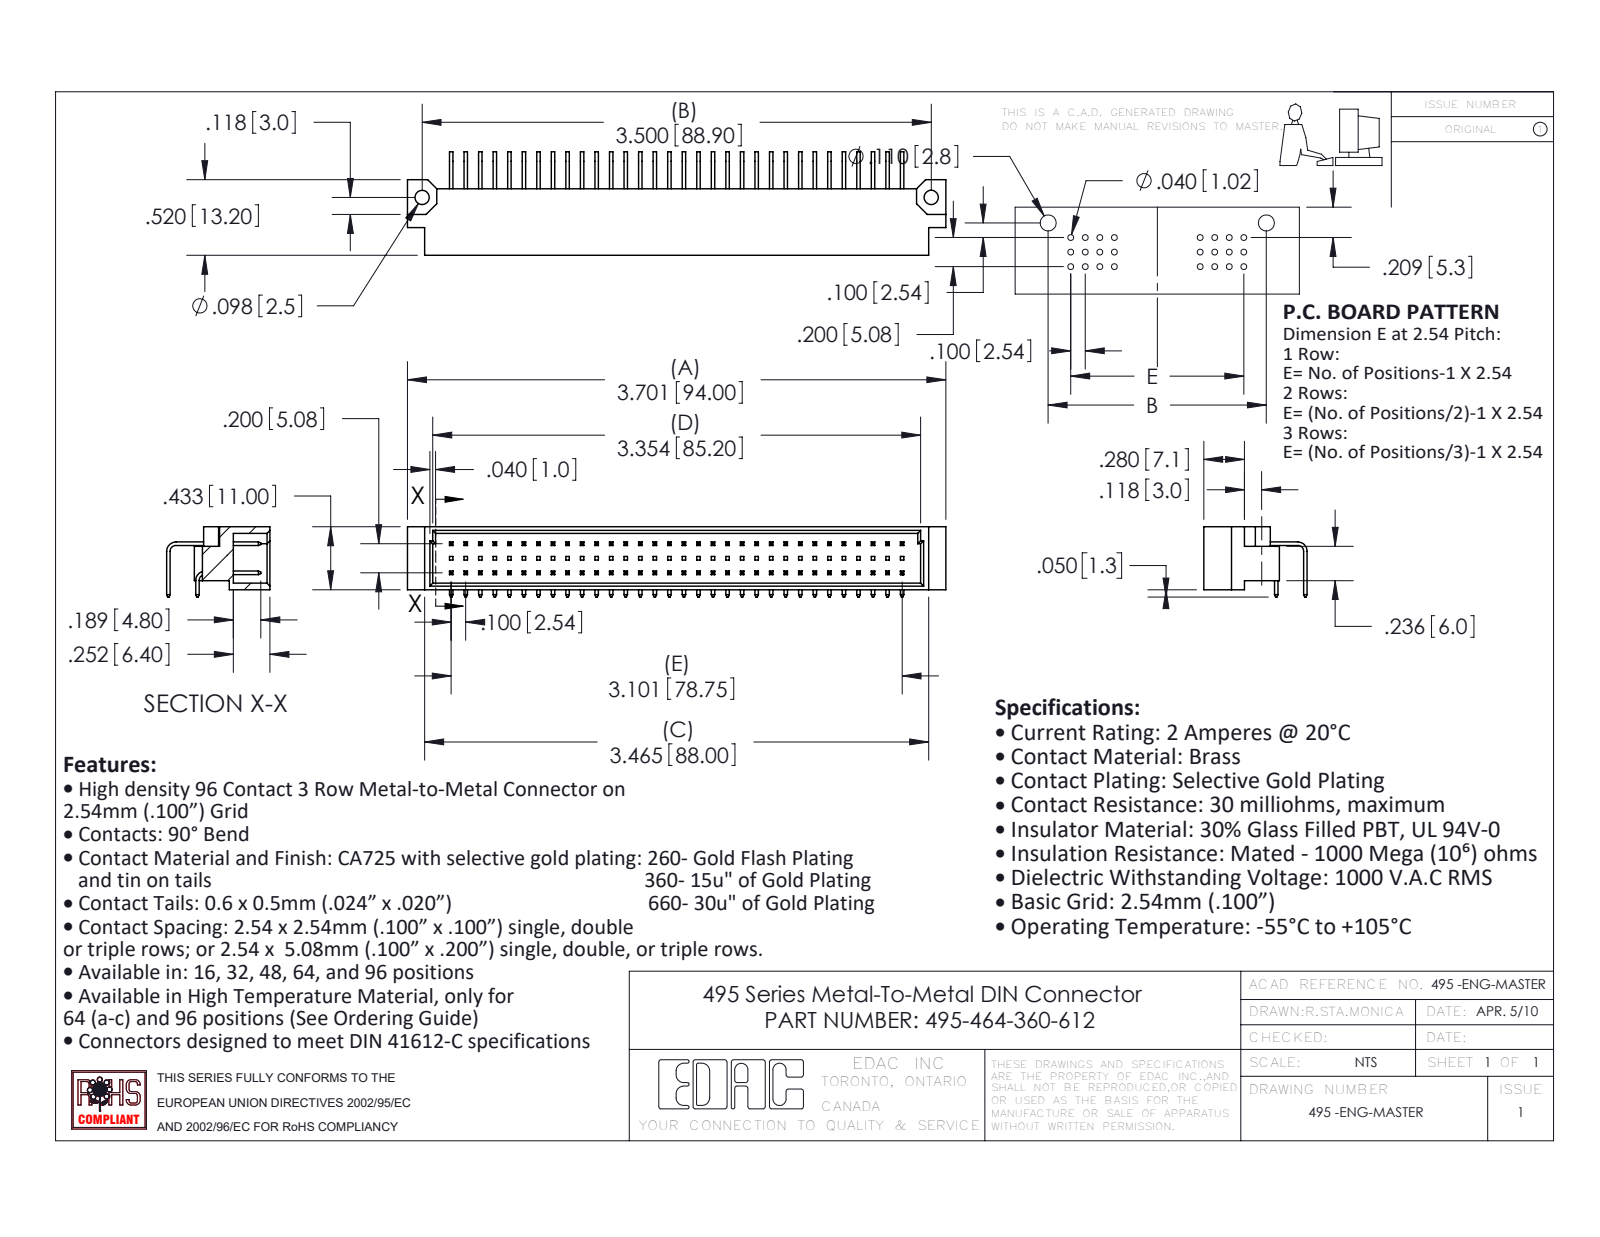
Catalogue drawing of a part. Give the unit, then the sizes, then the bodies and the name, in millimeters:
Units: millimetres
Overall size (bounding box): 94 × 18.05 × 12.27
Round holes (diameter × count): ⌀2.49 ×2
Partial cylindrical surfaces — rounded edges, fillets, slot ends (radius × count): R1.02 ×2, R1.65 ×2
Main face-to-face distances: 1.14, 9.86, 0.61, 5.08, 5.2, 11, 2.54, 8.72, 1.6, 9.4
Hole centre spacings: 88.9
Volume: 6 391 mm³ · Surface area: 9 910 mm²
Bodies: 65 solids, 1585 faces (1453 planar, 132 cylindrical, 0 other)
Part name (STEP PRODUCT): 495-290-3; 495-464-360-612; 495 Part_96; 495-290-1
STEP written by: SolidWorks 2020 (AUTOMOTIVE_DESIGN)
